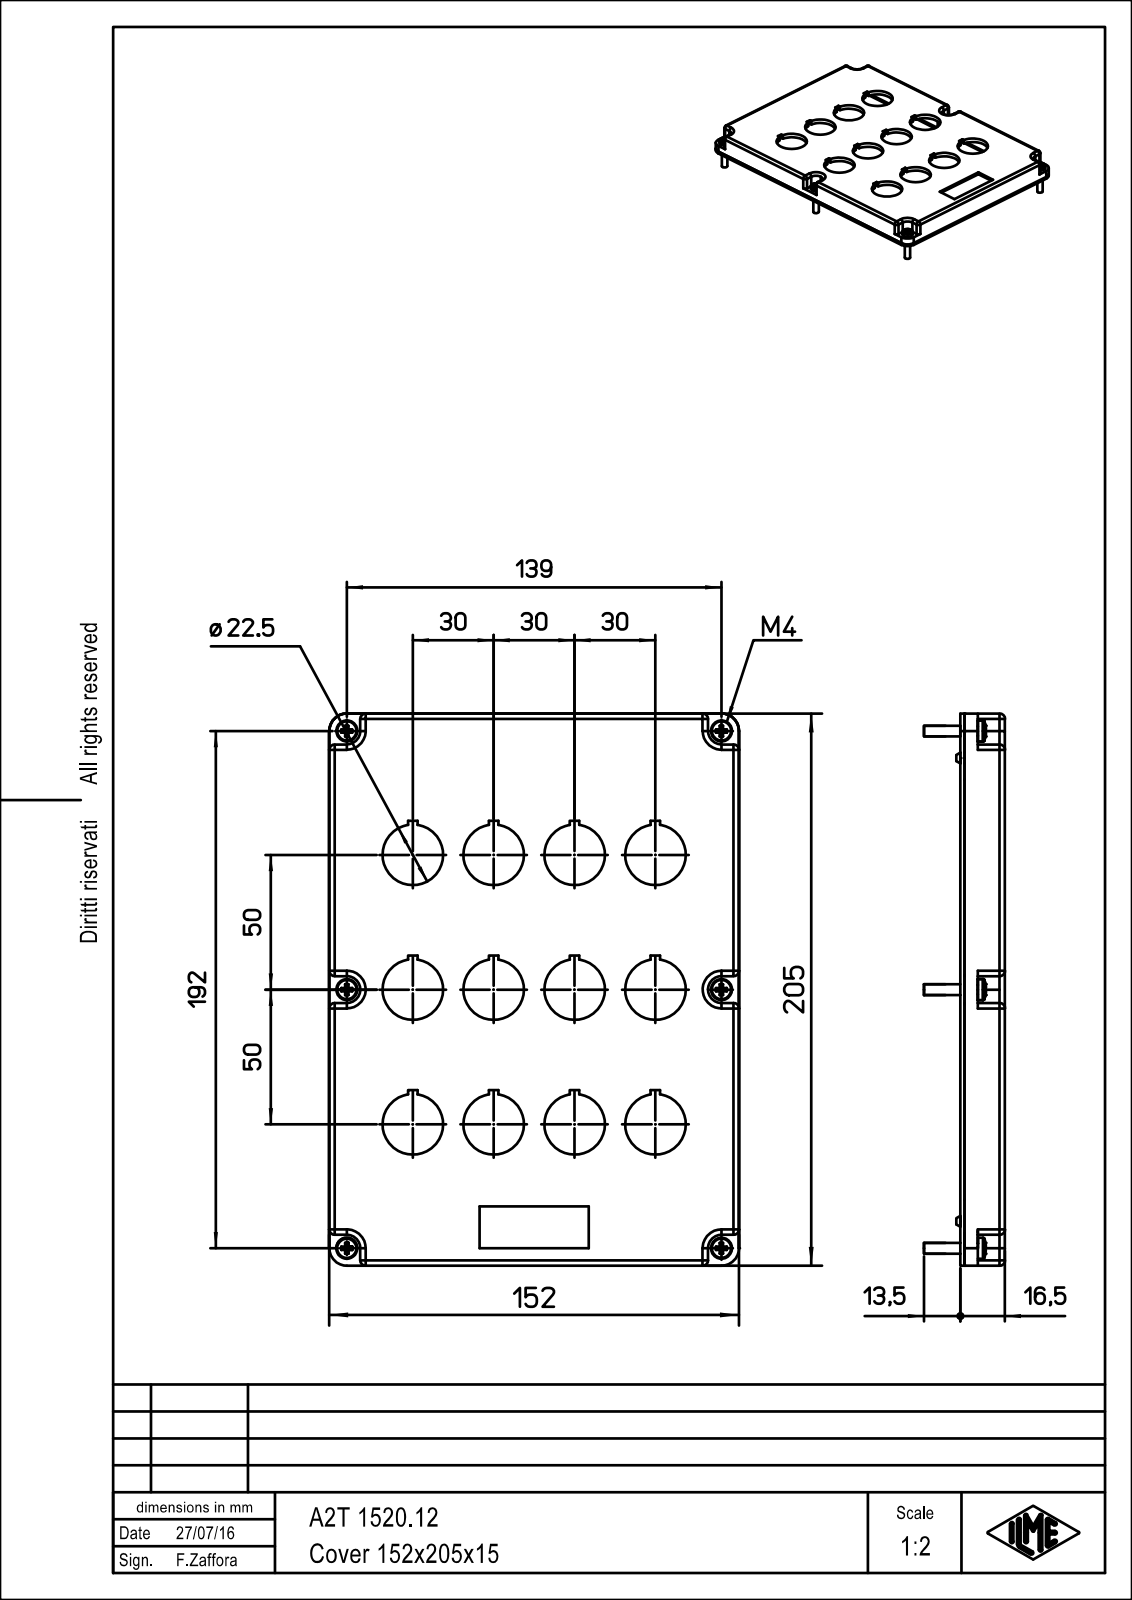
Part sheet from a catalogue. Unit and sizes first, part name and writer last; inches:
Units: inches
Overall size (bounding box): 8.071 × 5.985 × 1.181
Round holes (diameter × count): ⌀0.886 ×12, ⌀0.177 ×6, ⌀0.13 ×1, ⌀0.228 ×1
Round bosses / shafts (diameter × count): ⌀0.307 ×6, ⌀0.157 ×6, ⌀0.236 ×2, ⌀0.276 ×1, ⌀0.244 ×1
Partial cylindrical surfaces — rounded edges, fillets, slot ends (radius × count): R0.079 ×23, R0.013 ×11, R0.315 ×10, R0.256 ×8, R0.197 ×6, R0.011 ×2, R0.011 ×2, R0.02 ×2
Main face-to-face distances: 0.118, 0.531, 0.65, 0.059, 0.472, 0.591, 5.866, 7.953, 5.984, 8.071
Hole centre spacings: 2.296, 1.181, 1.969, 3.075, 2.362, 4.11, 2.052, 2.192
Volume: 7.662 in³ · Surface area: 138.5 in²
Bodies: 1 solid, 723 faces (517 planar, 152 cylindrical, 54 other)
Part name (STEP PRODUCT): A2T_1520.12
STEP written by: PTC Creo Elements/Direct Modeling 19.0B 21-Mar-2015 (C) Parametric Technology GmbH (AUTOMOTIVE_DESIGN)
